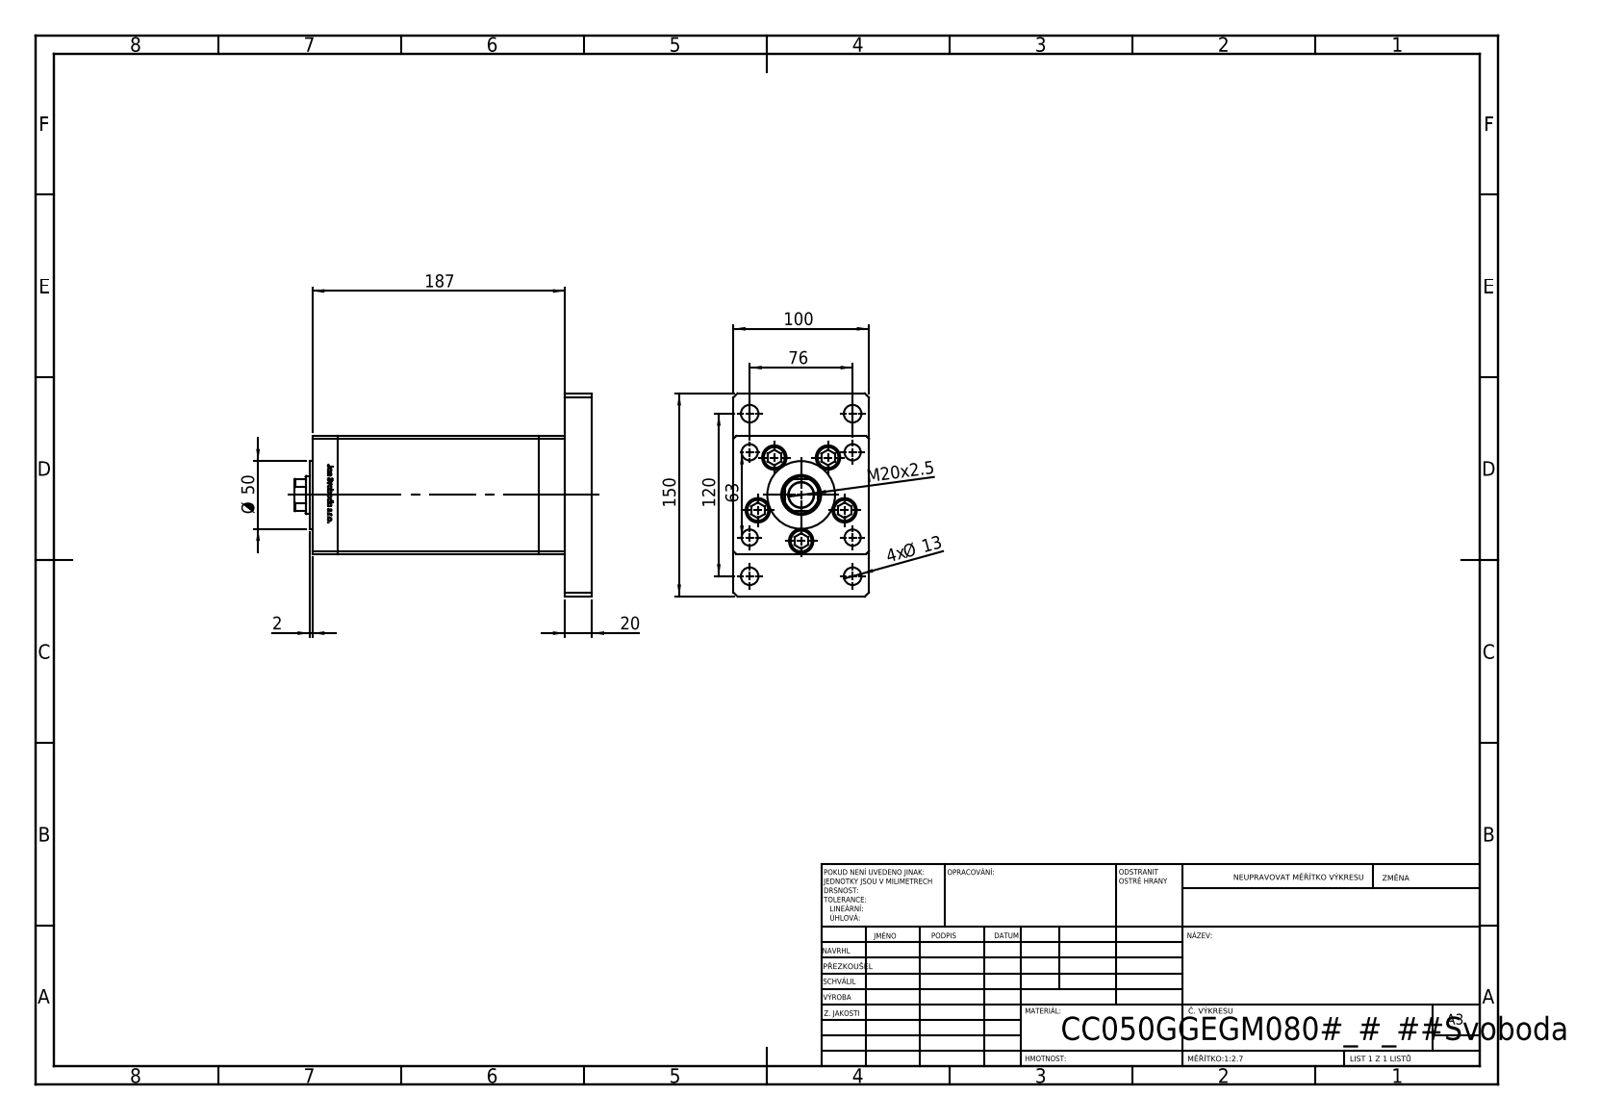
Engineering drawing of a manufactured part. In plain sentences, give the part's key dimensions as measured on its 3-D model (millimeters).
The part is named "V220C_FRONT_G; ALLEN BOLT; V220C_VC_G; V220C_G_MIDDLE (+2 more)". Its 3-D file was written by "SolidWorks 2019 (CONFIG_CONTROL_DESIGN)". It is 19 solids with 1310 faces: 517 planar, 187 cylindrical and 606 other. Overall it measures 219.5 by 150 by 100 millimeters. Its volume is 1 697 000 cubic millimeters and its surface area 256 566 square millimeters. Round holes: 9 of diameter 12, 5 of diameter 13.5, 5 of diameter 18, 4 of diameter 13, 4 of diameter 17, 2 of diameter 2, 2 of diameter 13.16, 1 of diameter 18.5, 1 of diameter 28, 1 of diameter 29.5, 1 of diameter 68. Round bosses or shafts: 9 of diameter 8, 5 of diameter 17, 1 of diameter 50. Partial cylindrical surfaces (rounded edges, fillets, slot ends): 2 of radius 0.93, 1 of radius 13.5. The main face-to-face distances are 19, 100, 167.5, 87, 148.5, 20, 187.5, 39, 206.5, 186.5. The hole center spacings are 34, 28.5, 49.36, 71.02, 76, 81.17, 91.5, 118.95.
